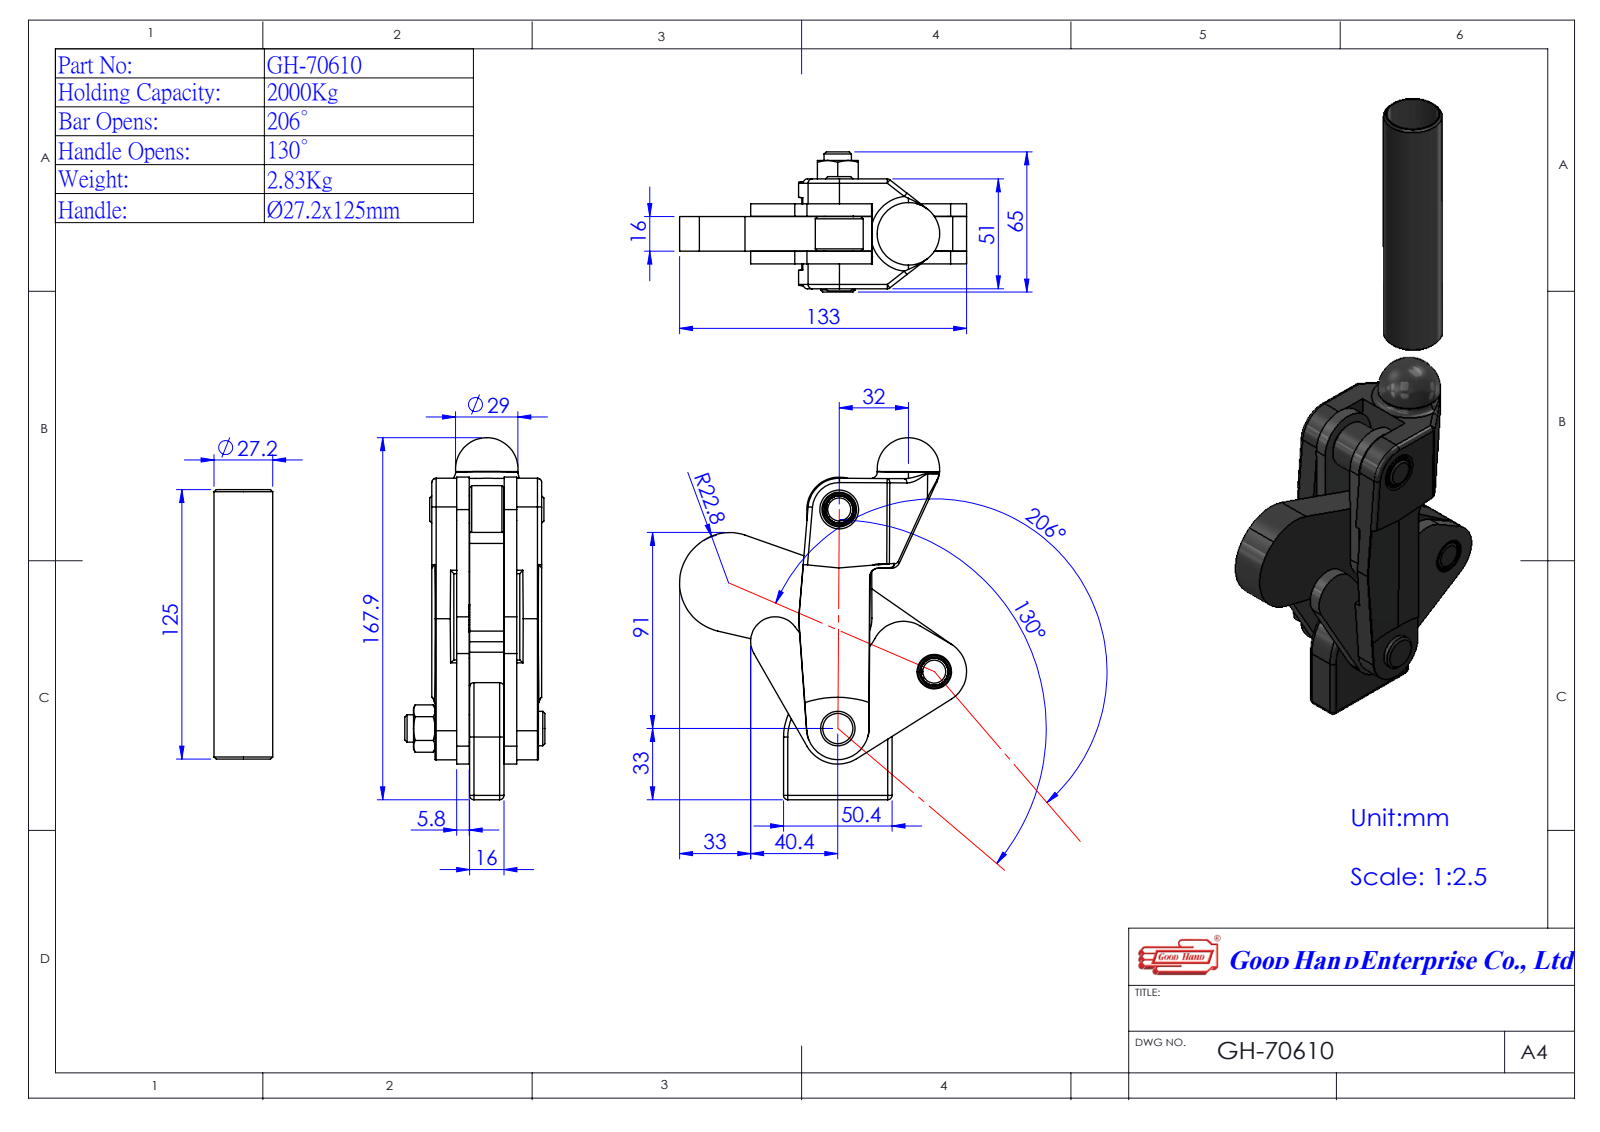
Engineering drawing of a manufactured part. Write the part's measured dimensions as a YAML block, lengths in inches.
part_name: "3700908-1^GH-70610(簡化); 3700929-1^GH-70610(簡化); GH-70610(簡化); Group1^GH-70610(簡化) (+3 more)"
step_written_by: "SolidWorks 2016 (AUTOMOTIVE_DESIGN)"
units: inches
bodies: {solids: 6, faces: 155, planar: 66, cylindrical: 71, other: 18}
overall_size: [11.534, 5.244, 2.559]
volume: 22.5
surface_area: 169.7
round_holes:
  - {diameter: 0.5, count: 3}
  - {diameter: 0.874, count: 1}
round_bosses_or_shafts:
  - {diameter: 0.63, count: 2}
  - {diameter: 0.498, count: 2}
  - {diameter: 1.071, count: 1}
  - {diameter: 0.874, count: 1}
  - {diameter: 0.5, count: 1}
partial_cylinders:
  - {radius: 0.571, count: 4}
  - {radius: 0.591, count: 4}
  - {radius: 0.157, count: 2}
  - {radius: 0.448, count: 1}
  - {radius: 0.65, count: 1}
  - {radius: 0.725, count: 1}
  - {radius: 0.866, count: 1}
  - {radius: 0.898, count: 1}
face_to_face_distances: [0.228, 0.868, 1.096, 0.689, 1.319, 0.64, 0.863, 0.635, 0.233, 0.233]
hole_center_spacings: [1.984, 2.012, 2.046]
